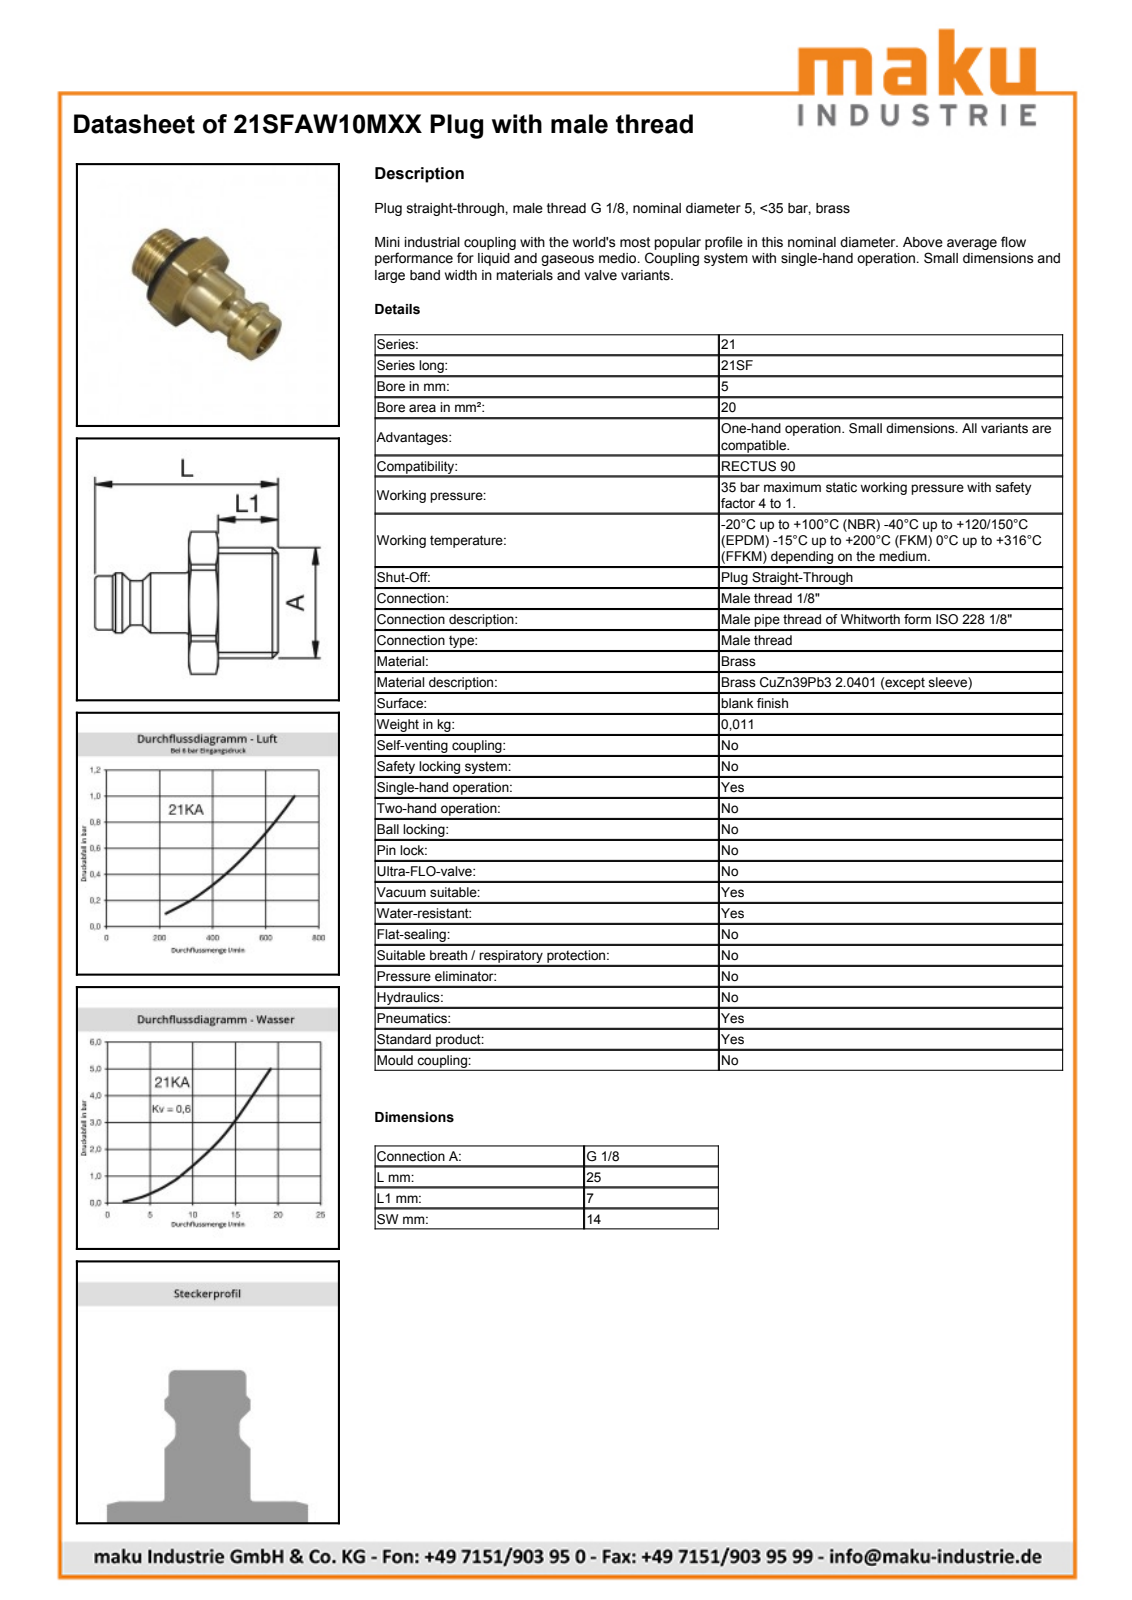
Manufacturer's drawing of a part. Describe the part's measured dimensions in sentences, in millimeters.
The part is named "D105315; D104294; D105313". Its 3-D file was written by "Autodesk Inventor 2011 (AUTOMOTIVE_DESIGN)". It is 2 solids with 50 faces: 14 planar, 15 cylindrical and 21 other. Overall it measures 25 by 15.8 by 14 millimeters. Its volume is 1 515 cubic millimeters and its surface area 1 656 square millimeters. Round holes: 1 of diameter 4.95. Round bosses or shafts: 1 of diameter 13, 1 of diameter 9.73, 1 of diameter 9, 1 of diameter 8.1, 1 of diameter 6.65. Partial cylindrical surfaces (rounded edges, fillets, slot ends): 1 of radius 4.95, 1 of radius 7.9. The main face-to-face distances are 14, 3.9, 5.4, 1.5, 14.1, 18, 19.5, 25, 10.9, 7.
